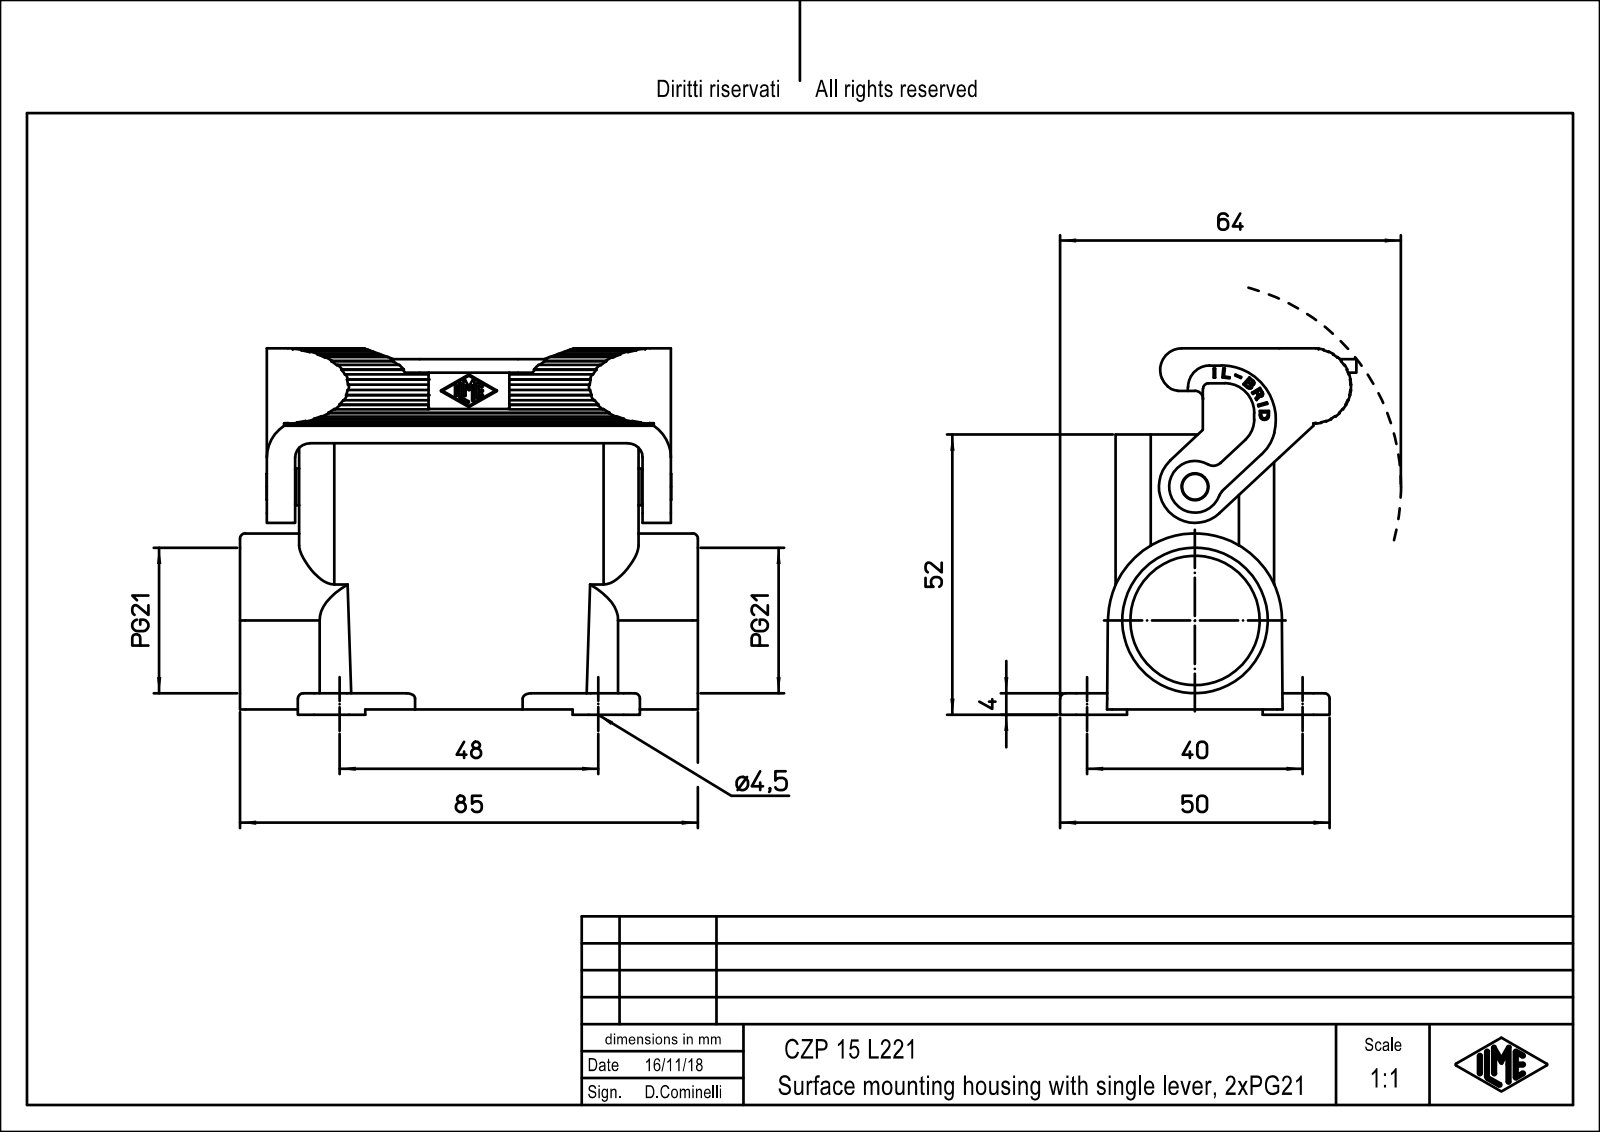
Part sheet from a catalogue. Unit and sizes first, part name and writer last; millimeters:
Units: millimetres
Overall size (bounding box): 85 × 68 × 55
Round holes (diameter × count): ⌀3 ×4, ⌀4.5 ×4, ⌀5 ×1, ⌀24 ×1, ⌀27 ×1
Round bosses / shafts (diameter × count): ⌀6.8 ×1, ⌀4.8 ×1
Partial cylindrical surfaces — rounded edges, fillets, slot ends (radius × count): R0.2 ×15, R1 ×13, R3 ×9, R6.5 ×4, R0.1 ×3, R0.3 ×2, R2 ×2, R2.8 ×2
Main face-to-face distances: 2.6, 26.8, 29.4, 24.2, 3, 33.2, 30.6, 6.4, 3.8, 5.25
Hole centre spacings: 12.02, 28.01, 50.21, 56.22, 16, 40, 48, 49.5
Volume: 52 229 mm³ · Surface area: 33 243 mm²
Bodies: 1 solid, 380 faces (193 planar, 169 cylindrical, 18 other)
Part name (STEP PRODUCT): CZP_15_L221
STEP written by: PTC Creo Elements/Direct Modeling 19.0E 27-Jun-2016 (C) Parametric Technology GmbH (AUTOMOTIVE_DESIGN)
